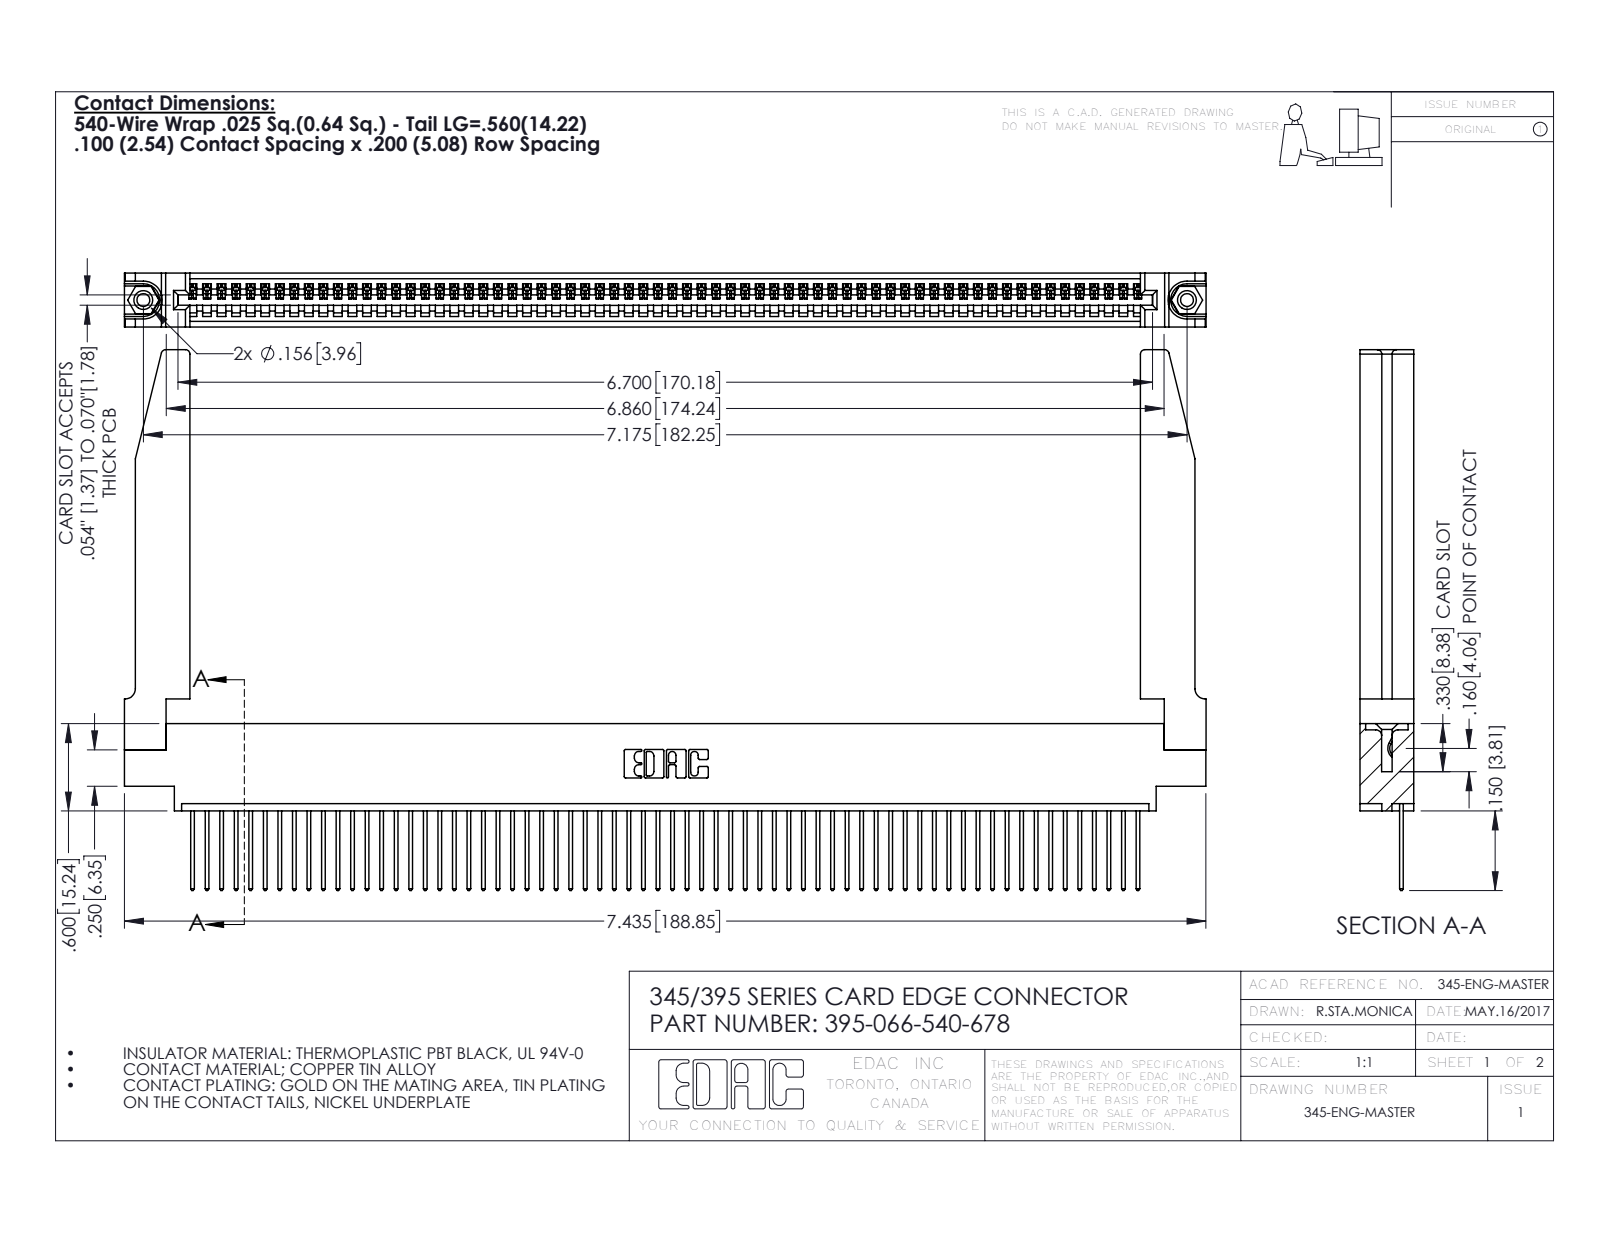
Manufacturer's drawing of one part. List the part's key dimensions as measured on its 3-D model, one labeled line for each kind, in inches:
Part name (STEP PRODUCT): 345-292-001_345-293-140; 395-066-540-678; 345 Part_0.170 Offset - 0.156 Dia-TH; 345-220-078_345-220-078 (+1 more)
STEP written by: SolidWorks 2016 (CONFIG_CONTROL_DESIGN)
Units: inches
Bodies: 71 solids, 4192 faces (2866 planar, 1274 cylindrical, 52 other)
Overall size (bounding box): 7.436 × 3.717 × 0.37
Volume: 1.579 in³ · Surface area: 49.62 in²
Round holes (diameter × count): ⌀0.089 ×2, ⌀0.125 ×2, ⌀0.156 ×2, ⌀0.064 ×1
Round bosses / shafts (diameter × count): ⌀0.155 ×2
Partial cylindrical surfaces — rounded edges, fillets, slot ends (radius × count): R0.006 ×132, R0.01 ×132, R0.01 ×22, R0.03 ×8, R0.007 ×6, R0.031 ×6, R0.026 ×3, R0.031 ×2
Main face-to-face distances: 0.072, 0.37, 0.298, 0.098, 0.272, 0.025, 0.2, 0.225, 0.175, 0.15
Hole centre spacings: 0.27, 6.939, 7.175
